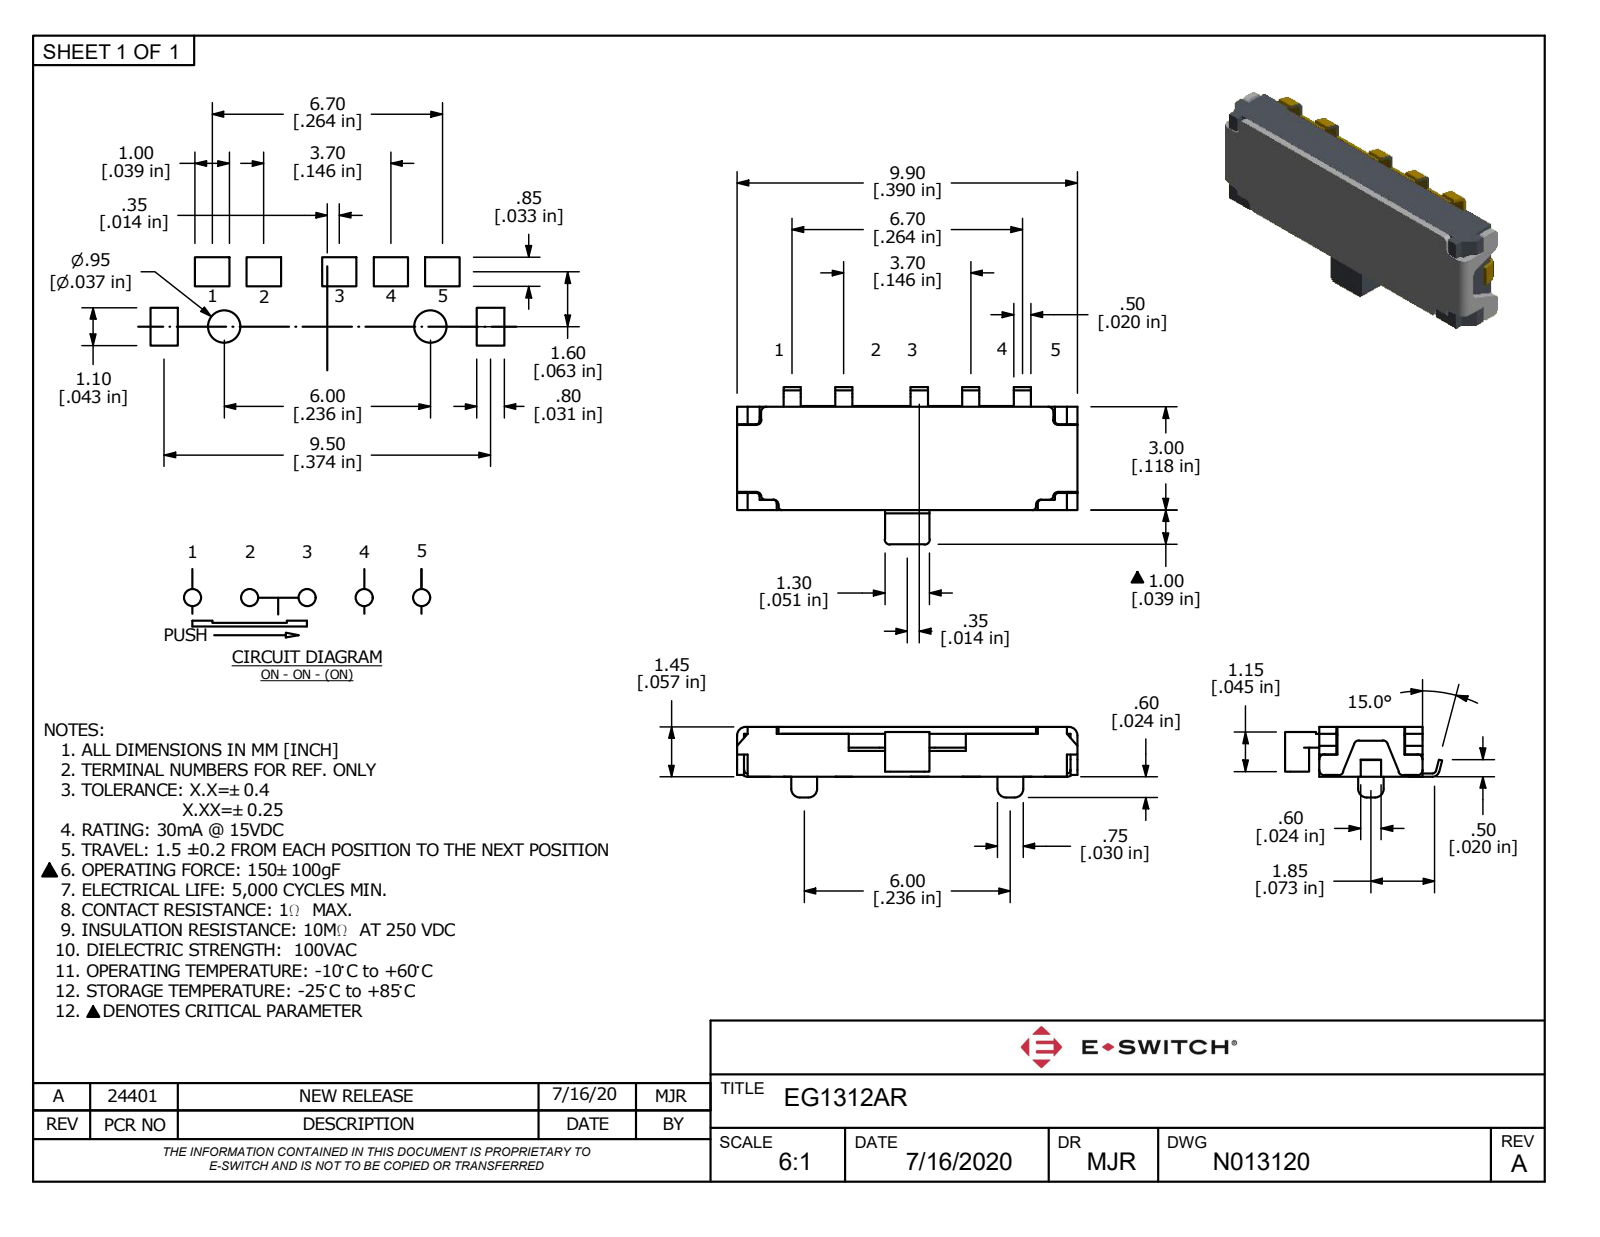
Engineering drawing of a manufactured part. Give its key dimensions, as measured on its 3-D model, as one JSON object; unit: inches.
{"part_name": "EG1312AR", "step_written_by": "Autodesk Inventor 2020 (AUTOMOTIVE_DESIGN)", "units": "inches", "bodies": {"solids": 1, "faces": 249, "planar": 177, "cylindrical": 70, "other": 2}, "overall_size": [0.39, 0.18, 0.081], "volume_in3": 0.002, "surface_area_in2": 0.288, "round_bosses_or_shafts": [[0.03, 2]], "partial_cylinders_radius": [[0.006, 35], [0.004, 11], [0.008, 4], [0.01, 2]], "face_to_face_distances": [0.057, 0.02, 0.03, 0.037, 0.016, 0.014, 0.024, 0.028, 0.118, 0.033]}
